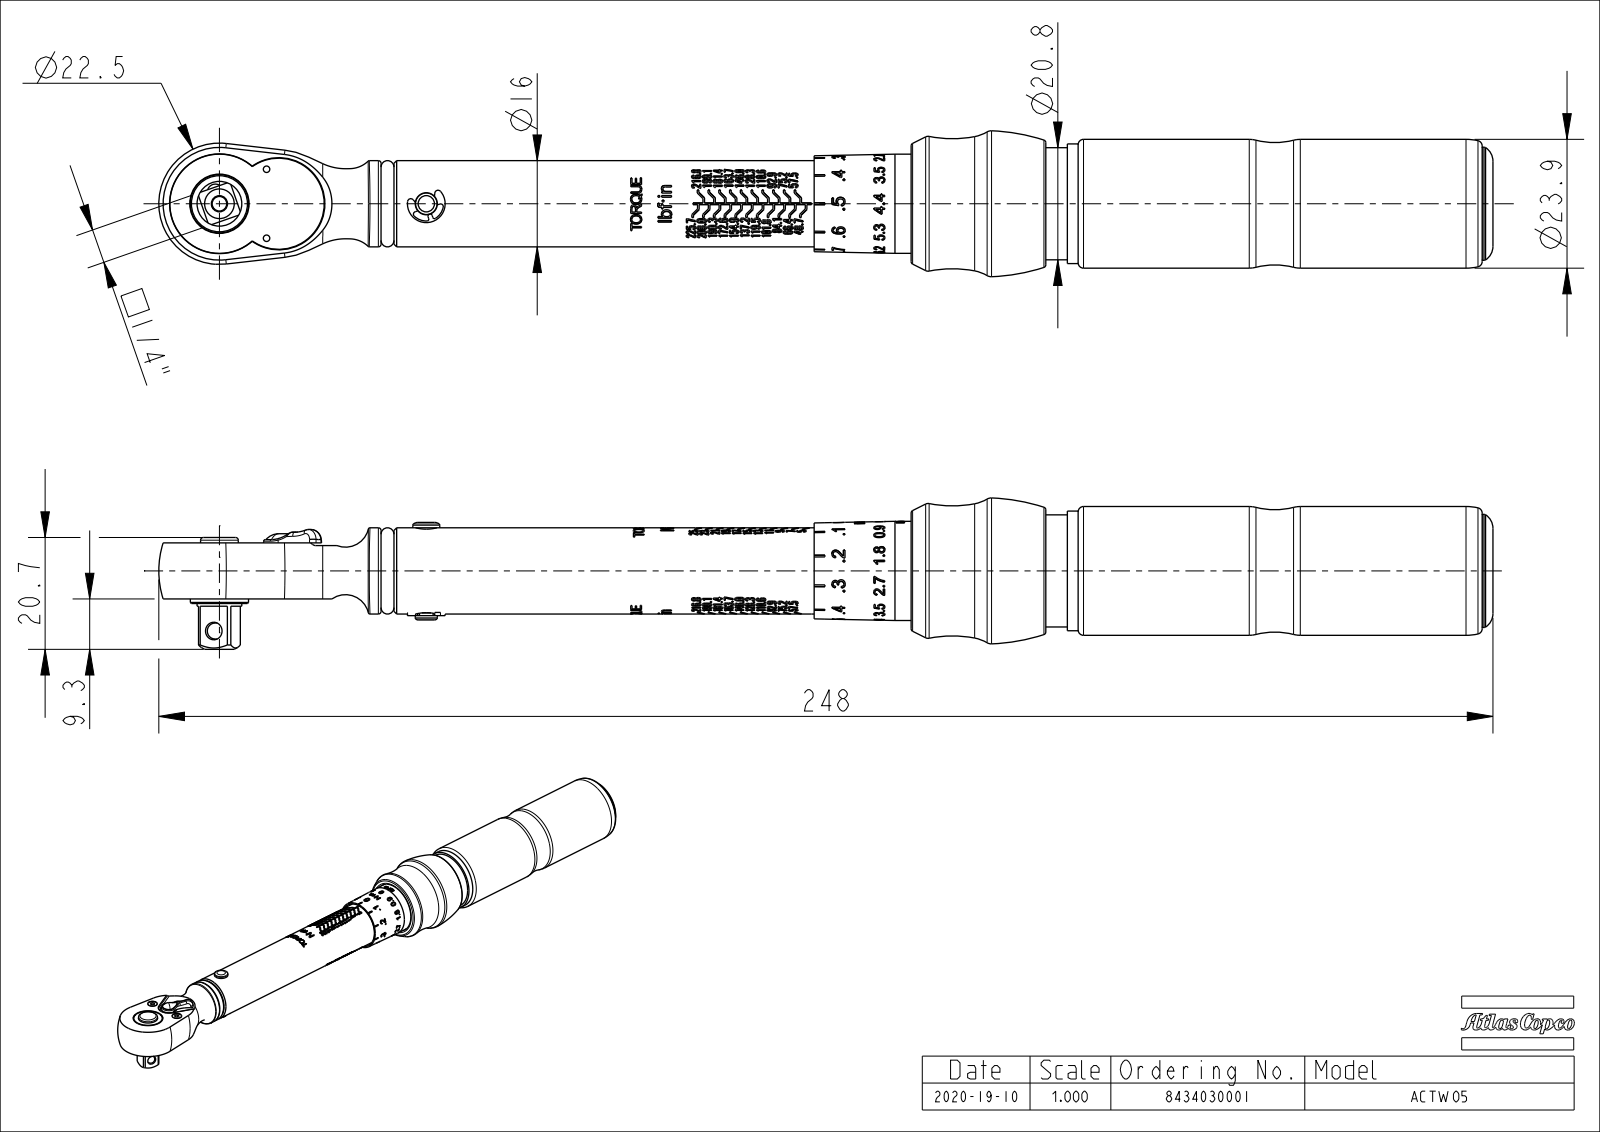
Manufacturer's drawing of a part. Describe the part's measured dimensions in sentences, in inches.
The part is named "ASM0003_SW0002". Its 3-D file was written by "CREO PARAMETRIC BY PTC INC, 2018100 (CONFIG_CONTROL_DESIGN)". It is 2 solids with 3737 faces: 1410 planar, 317 cylindrical and 2010 other. Overall it measures 9.75 by 1.106 by 1.066 inches. Its volume is 4.692 cubic inches and its surface area 27.73 square inches. Round holes: 2 of diameter 0.047, 2 of diameter 0.098, 2 of diameter 0.142, 1 of diameter 0.128, 1 of diameter 0.228, 1 of diameter 0.433. Round bosses or shafts: 1 of diameter 0.941, 1 of diameter 0.874, 1 of diameter 0.826, 1 of diameter 0.819, 1 of diameter 0.724, 1 of diameter 0.63, 1 of diameter 0.433, 1 of diameter 0.431. Partial cylindrical surfaces (rounded edges, fillets, slot ends): 2 of radius 0.005, 2 of radius 0.008, 2 of radius 0.013, 2 of radius 0.019, 2 of radius 0.024, 2 of radius 0.031, 2 of radius 0.681, 1 of radius 0.016. The main face-to-face distances are 0.409, 0.02, 0.39, 8.126, 0.25, 0.079, 3.874, 4.252, 5.016, 1.142. The hole center spacings are 0.267, 0.427, 0.434, 0.504.
